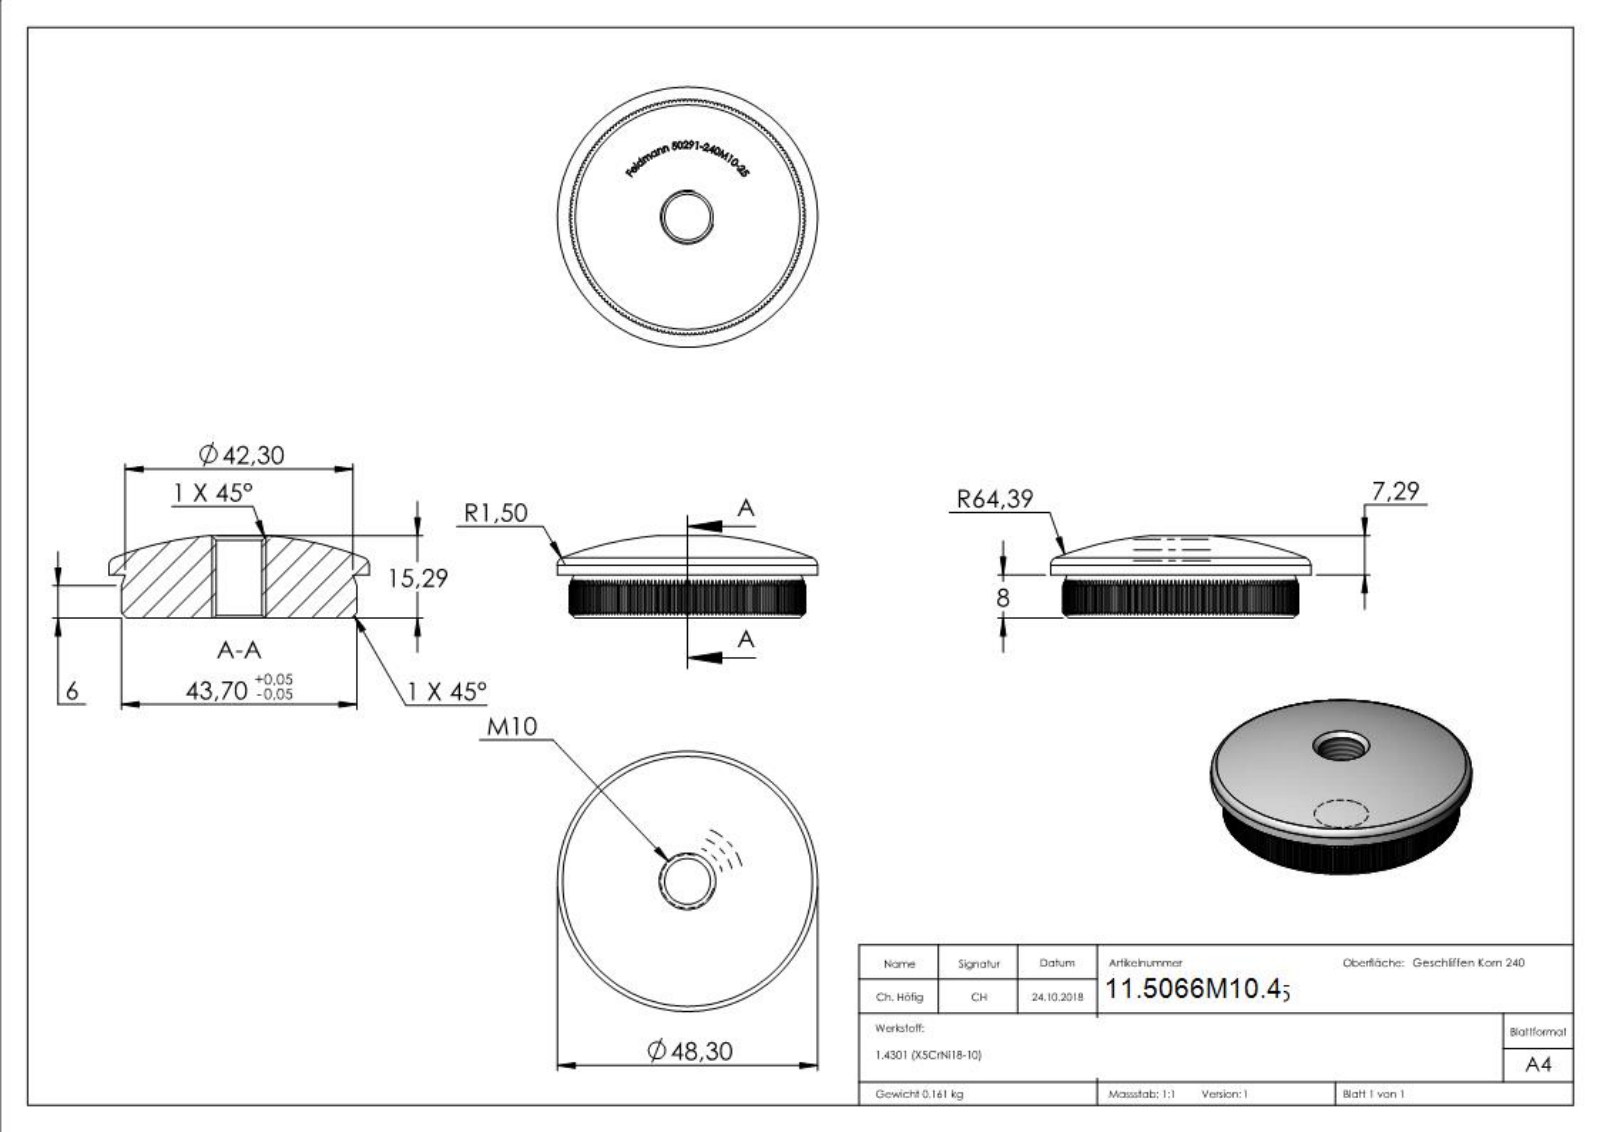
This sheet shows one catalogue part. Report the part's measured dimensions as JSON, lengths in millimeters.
{"part_name": "50291-240M10-25", "step_written_by": "SolidWorks 2015 (CONFIG_CONTROL_DESIGN)", "units": "millimeters", "bodies": {"solids": 1, "faces": 813, "planar": 512, "cylindrical": 194, "other": 107}, "overall_size": [48.3, 48.3, 15.29], "volume_mm3": 20332, "surface_area_mm2": 5953, "round_holes": [[8.5, 1]], "round_bosses_or_shafts": [[48.3, 1]], "partial_cylinders_radius": [[21.85, 1]], "face_to_face_distances": [8, 21.5, 21.48, 21.52, 7.9, 0.66, 0.54, 0.67, 0.79, 0.72]}
